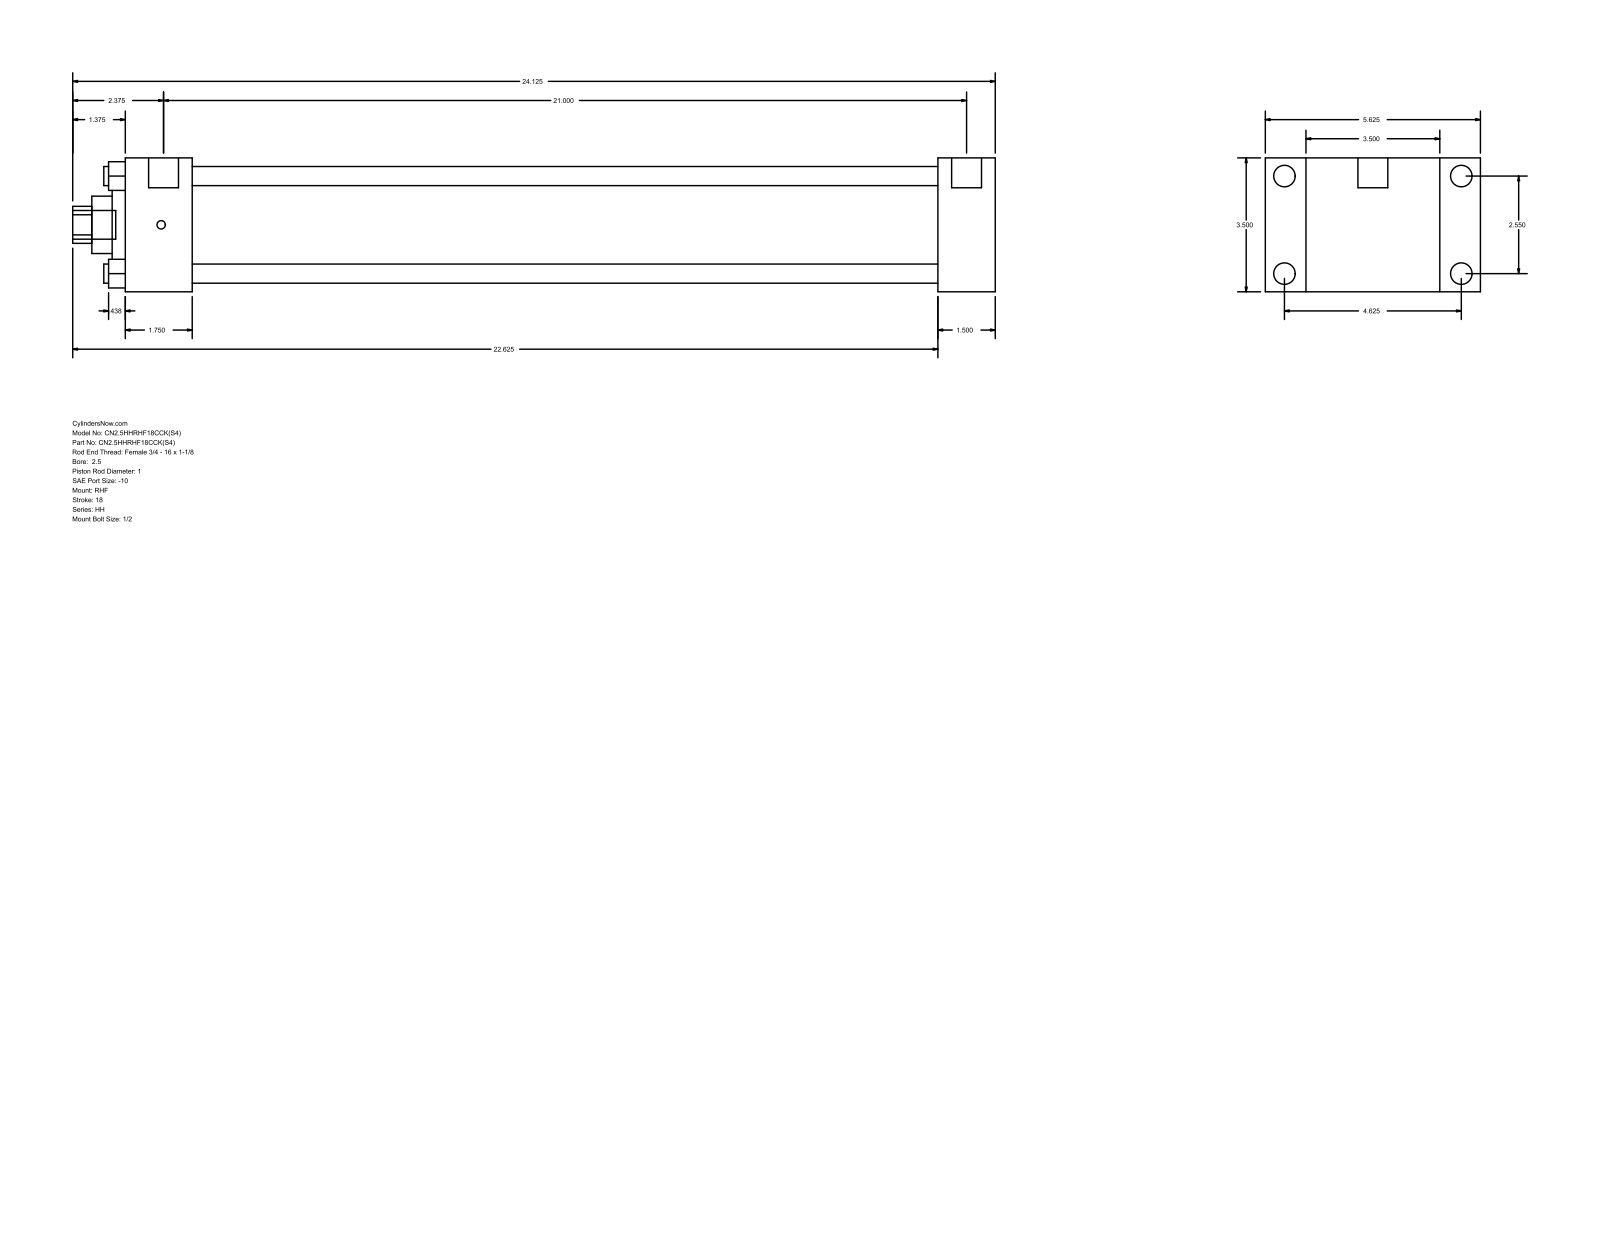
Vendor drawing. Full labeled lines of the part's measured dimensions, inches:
Part name (STEP PRODUCT): HH_RHF__0250_1
STEP written by: GSSL Pune (CONFIG_CONTROL_DESIGN)
Units: inches
Bodies: 0 solids, 90 faces (61 planar, 29 cylindrical, 0 other)
Overall size (bounding box): 24.125 × 5.625 × 3.5
Round holes (diameter × count): ⌀0.5 ×4, ⌀1 ×1, ⌀1.5 ×1, ⌀2.375 ×1, ⌀2.875 ×1
Round bosses / shafts (diameter × count): ⌀0.563 ×4, ⌀0.219 ×4, ⌀0.781 ×2, ⌀0.75 ×1
Partial cylindrical surfaces — rounded edges, fillets, slot ends (radius × count): R0.484 ×1
Main face-to-face distances: 3.5, 1.5, 1.063, 4.563, 21.25, 22.75, 5.625, 1.75, 19.5, 21
Hole centre spacings: 1.803, 2.55, 3.606
